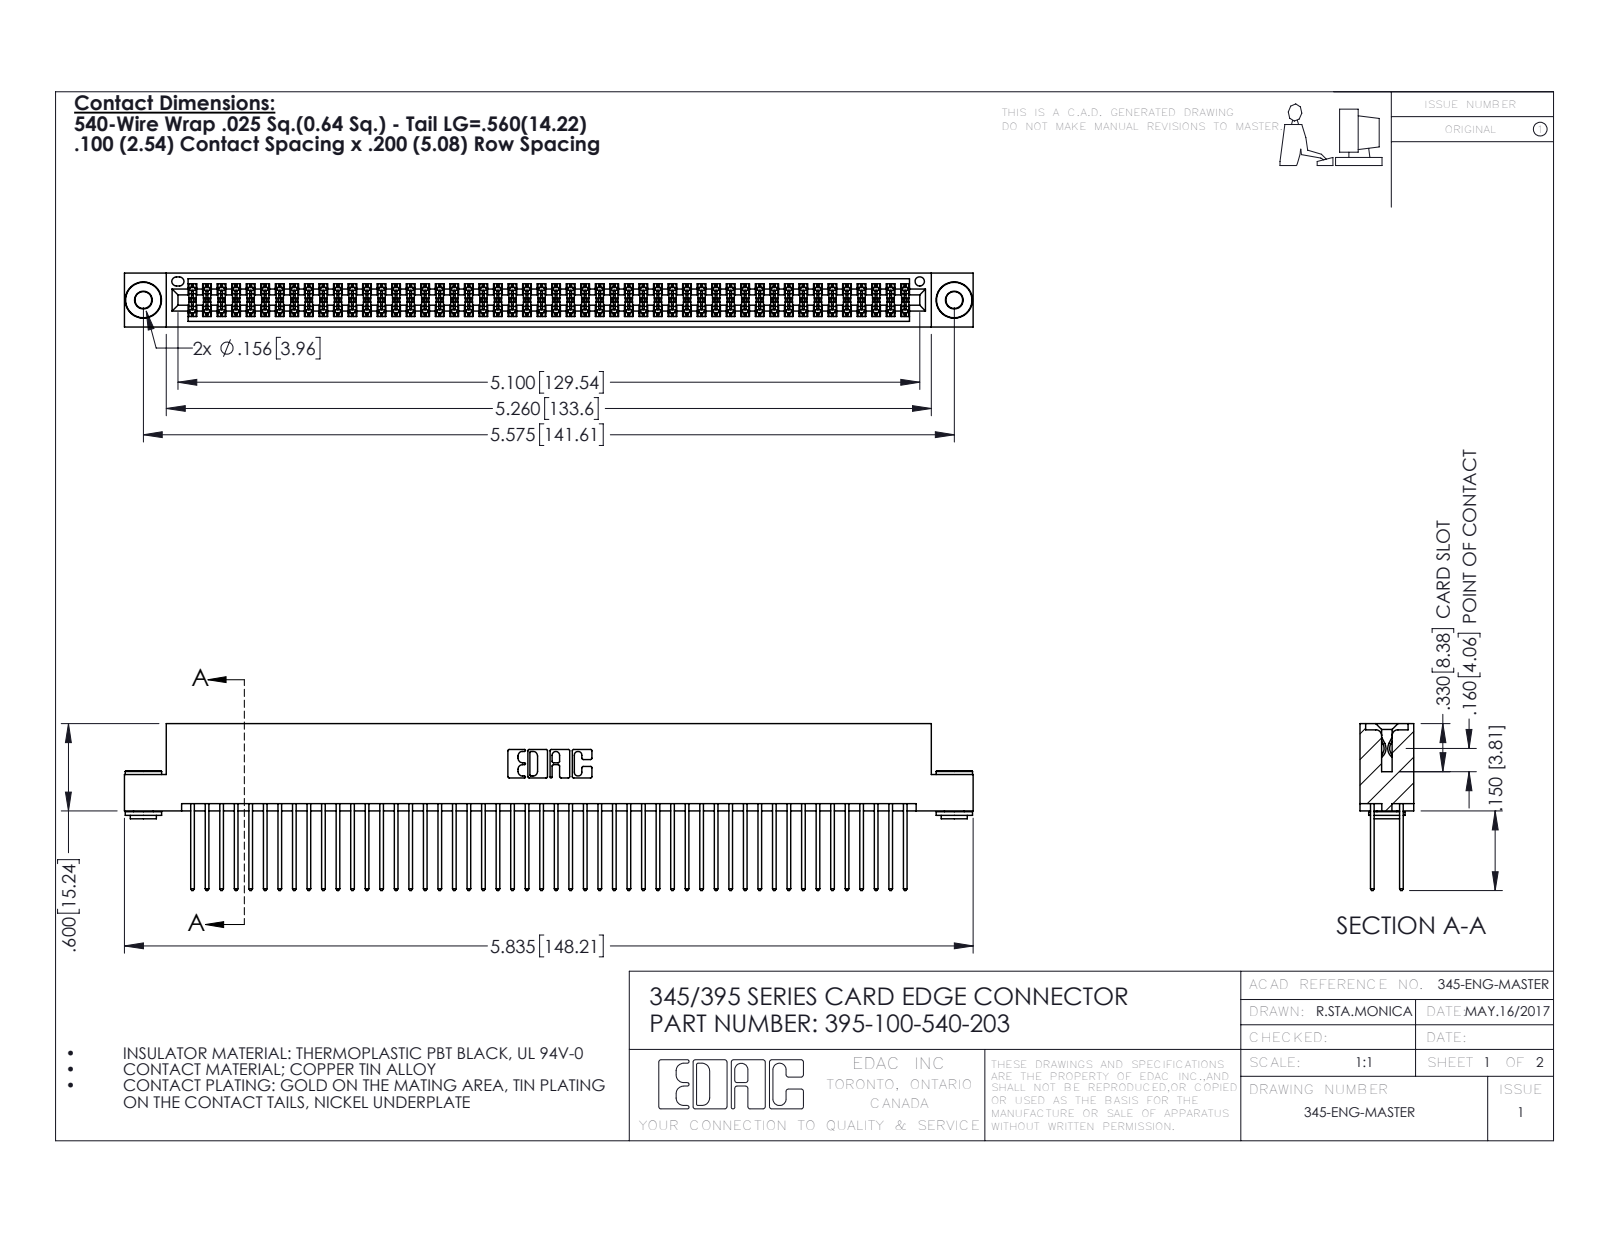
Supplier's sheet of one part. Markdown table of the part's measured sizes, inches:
| quantity | value |
| --- | --- |
| part name | 395-100-540-203; 345 Part_Flush Mounting Lugs - 0.156 Dia-TH; 345-250-002_345-250-002-102; 345-292-001_345-293-140 |
| STEP written by | SolidWorks 2016 (CONFIG_CONTROL_DESIGN) |
| units | inches |
| bodies | 103 solids, 5164 faces (3390 planar, 1766 cylindrical, 8 other) |
| overall size | 5.835 × 1.147 × 0.37 |
| volume | 0.907 in³ |
| surface area | 37.35 in² |
| round holes (diameter × count) | 0.116 × 2, 0.156 × 2, 0.064 × 1 |
| round bosses / shafts (diameter × count) | 0.25 × 2, 0.18 × 2, 0.136 × 2 |
| partial cylindrical surfaces (radius × count) | 0.006 × 150, 0.01 × 100, 0.01 × 22, 0.007 × 6, 0.031 × 6, 0.026 × 3, 0.014 × 2, 0.019 × 2 |
| main face-to-face distances | 0.072, 0.298, 0.2, 0.025, 0.098, 0.272, 0.225, 0.37, 0.175, 0.149 |
| hole center spacings | 0.27, 5.339, 5.575 |
